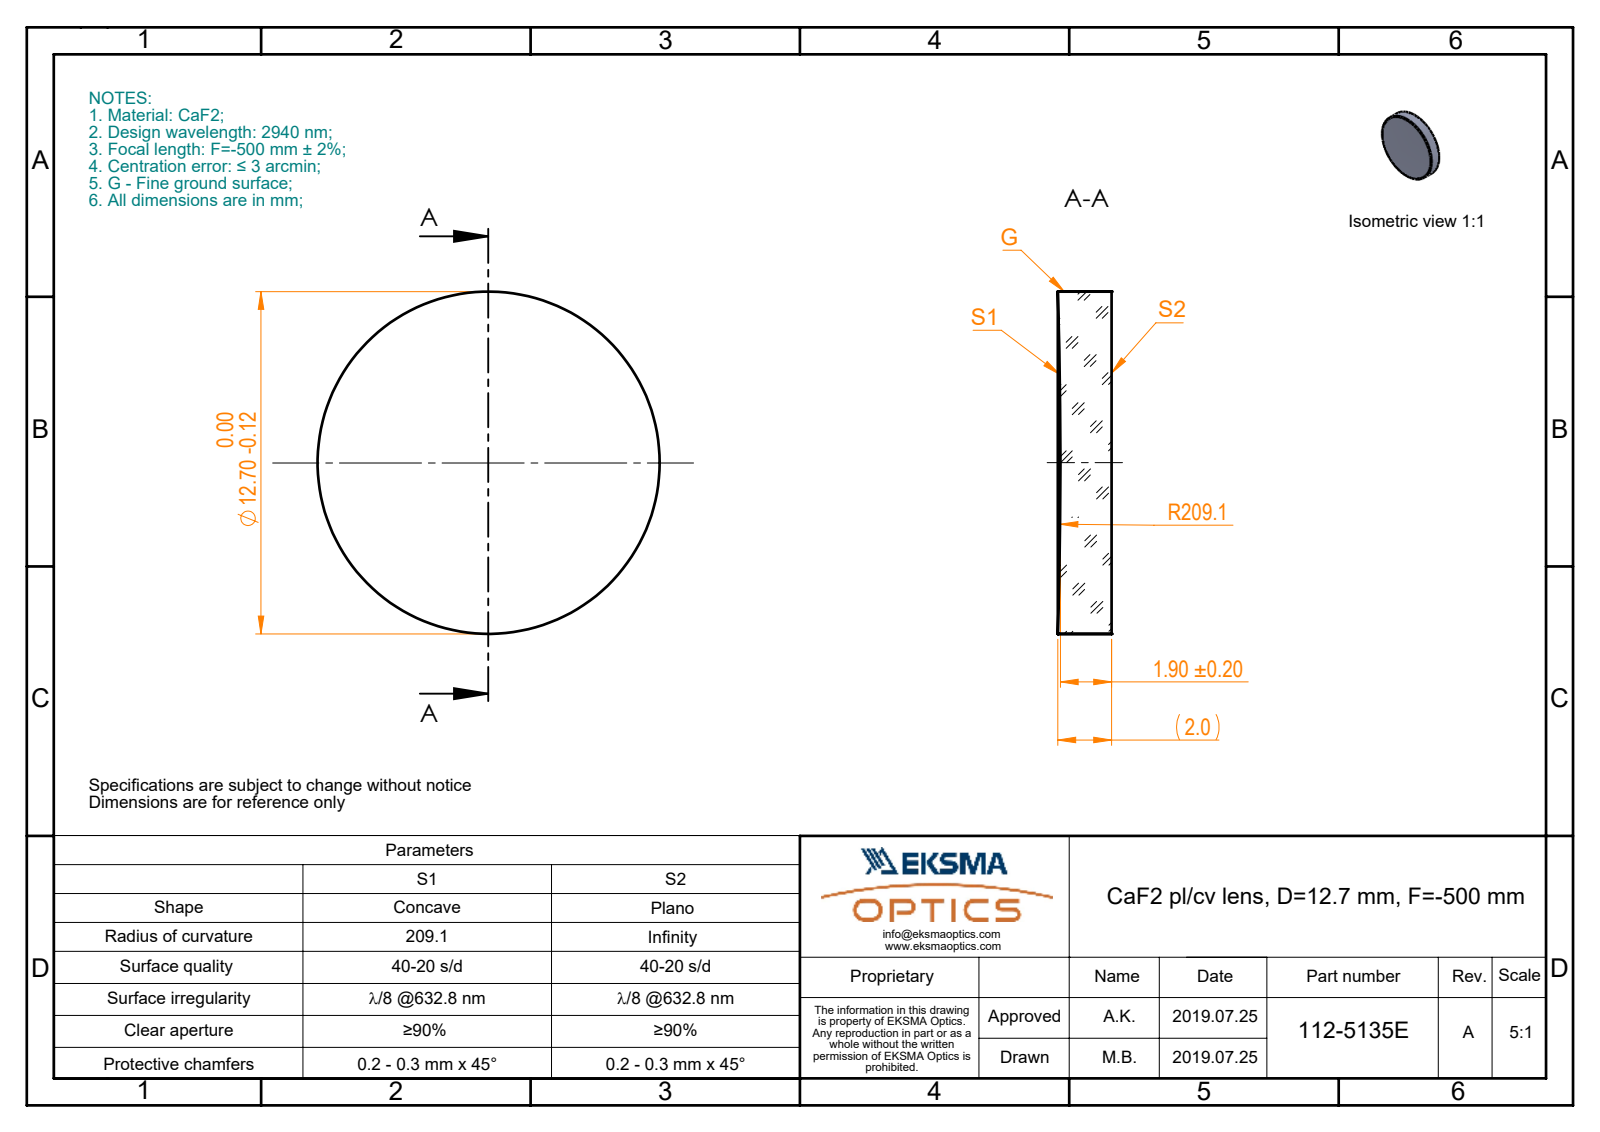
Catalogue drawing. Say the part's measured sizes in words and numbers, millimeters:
The part is named "112-5135E CaF2 pl-cv 12.7 F-500". Its 3-D file was written by "SolidWorks 2017 (CONFIG_CONTROL_DESIGN)". It is 1 solid with 5 faces: 1 planar, 2 cylindrical and 2 other. Overall it measures 12.7 by 12.7 by 2 millimeters. Its volume is 247 cubic millimeters and its surface area 333 square millimeters. Round bosses or shafts: 1 of diameter 12.7.
